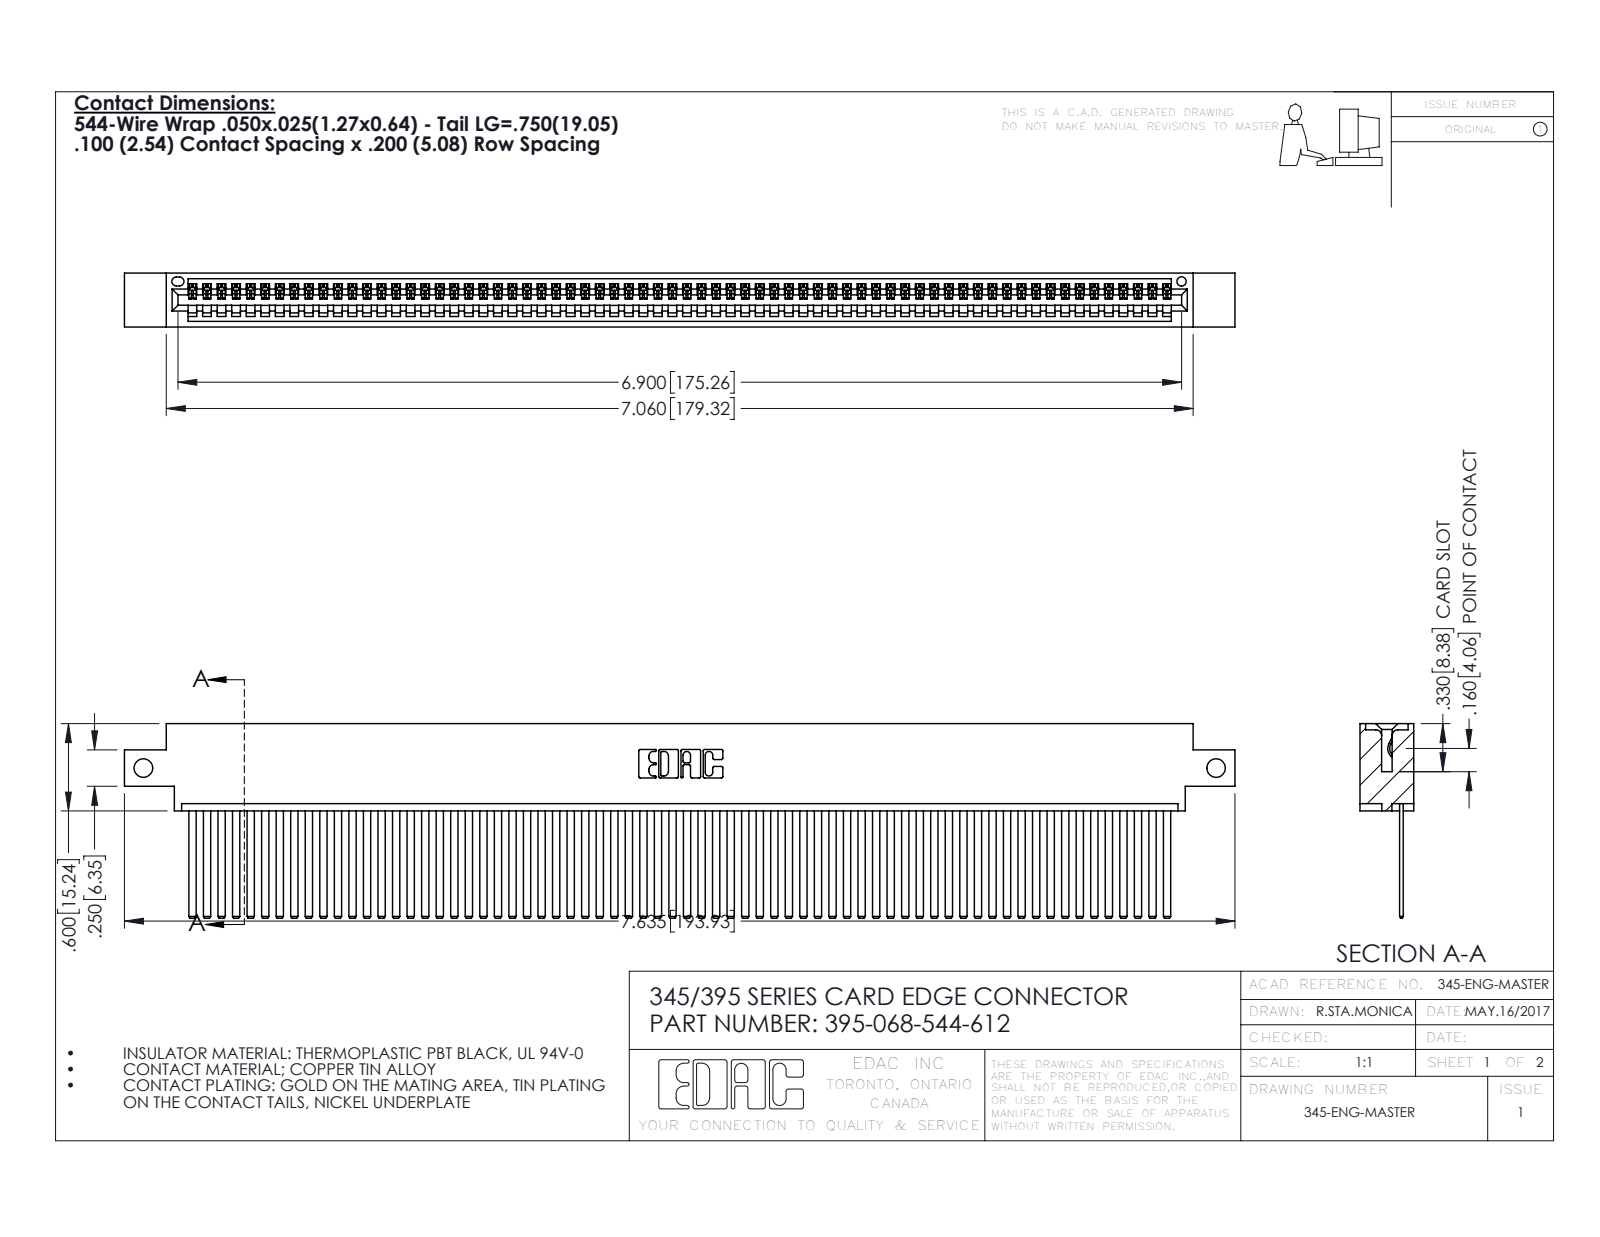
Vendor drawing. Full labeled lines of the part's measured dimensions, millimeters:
Part name (STEP PRODUCT): 395-068-544-612; 345-292-001_345-293-144; 345 Part_0.170 Offset - Side Mount
STEP written by: SolidWorks 2016 (CONFIG_CONTROL_DESIGN)
Units: millimetres
Bodies: 69 solids, 3666 faces (2532 planar, 1134 cylindrical, 0 other)
Overall size (bounding box): 193.9 × 34 × 9.4
Volume: 19 220 mm³ · Surface area: 28 250 mm²
Round holes (diameter × count): ⌀3.3 ×2, ⌀1.6 ×1
Partial cylindrical surfaces — rounded edges, fillets, slot ends (radius × count): R0.2 ×136, R0.3 ×22, R0.2 ×6, R0.8 ×6, R0.7 ×3, R0.8 ×2, R1 ×2, R0.4 ×1
Main face-to-face distances: 1.8, 7.6, 0.6, 2.5, 6.9, 9.4, 5.1, 5.7, 4.4, 3.8
Hole centre spacings: 187.3
